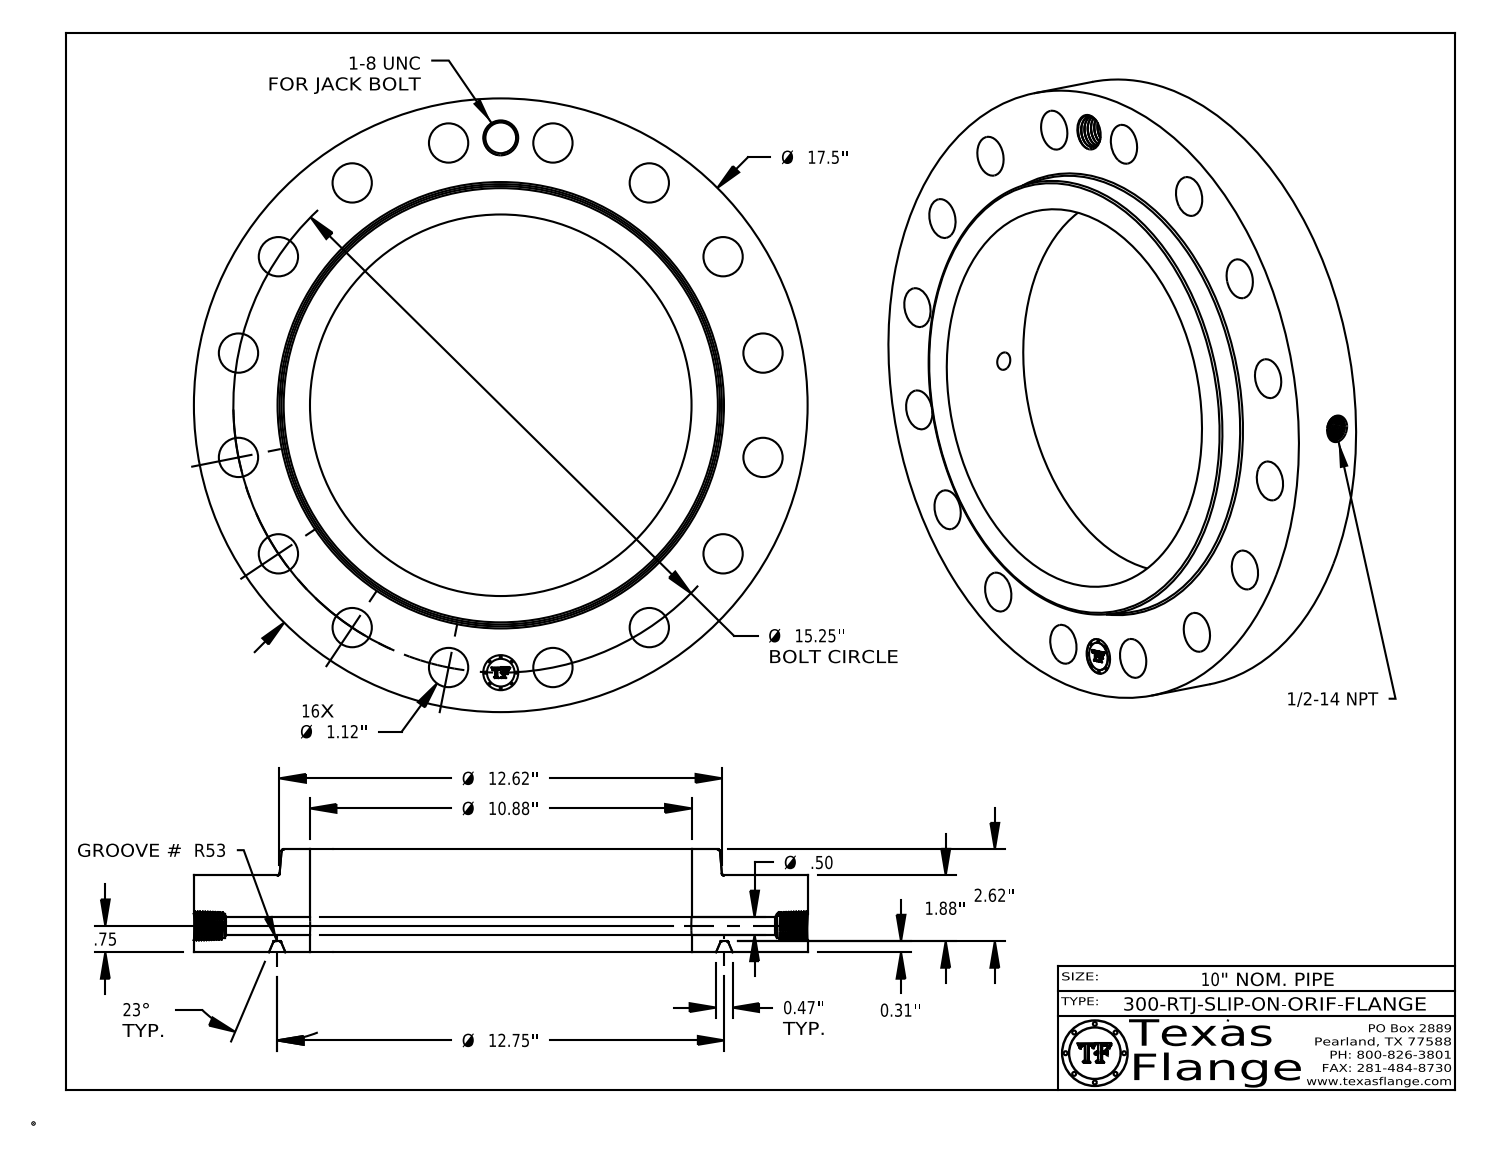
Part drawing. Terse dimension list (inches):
name: 300-RTJ-SLIP-ON
written by: CATIA V5 STEP AP214 (AUTOMOTIVE_DESIGN)
unit: in
bodies: 1 solid, 807 faces (370 planar, 110 cylindrical, 327 other)
size: 17.5 × 17.5 × 2.933
volume: 304.4 in³; area: 670.8 in²
holes: 16× ⌀1.12, 1× ⌀0.5, 1× ⌀0.672, 1× ⌀0.875, 1× ⌀1, 1× ⌀10.88
bosses: 8× ⌀0.061, 1× ⌀17.5, 1× ⌀0.788
face distances: 2.193, 2.933, 0.74, 0.313, 1.88, 2.62, 0.015, 2.178, 1.865, 0.755
hole spacings: 5.836, 7.625, 10.783, 14.089, 14.957, 2.975, 2.975, 8.472
